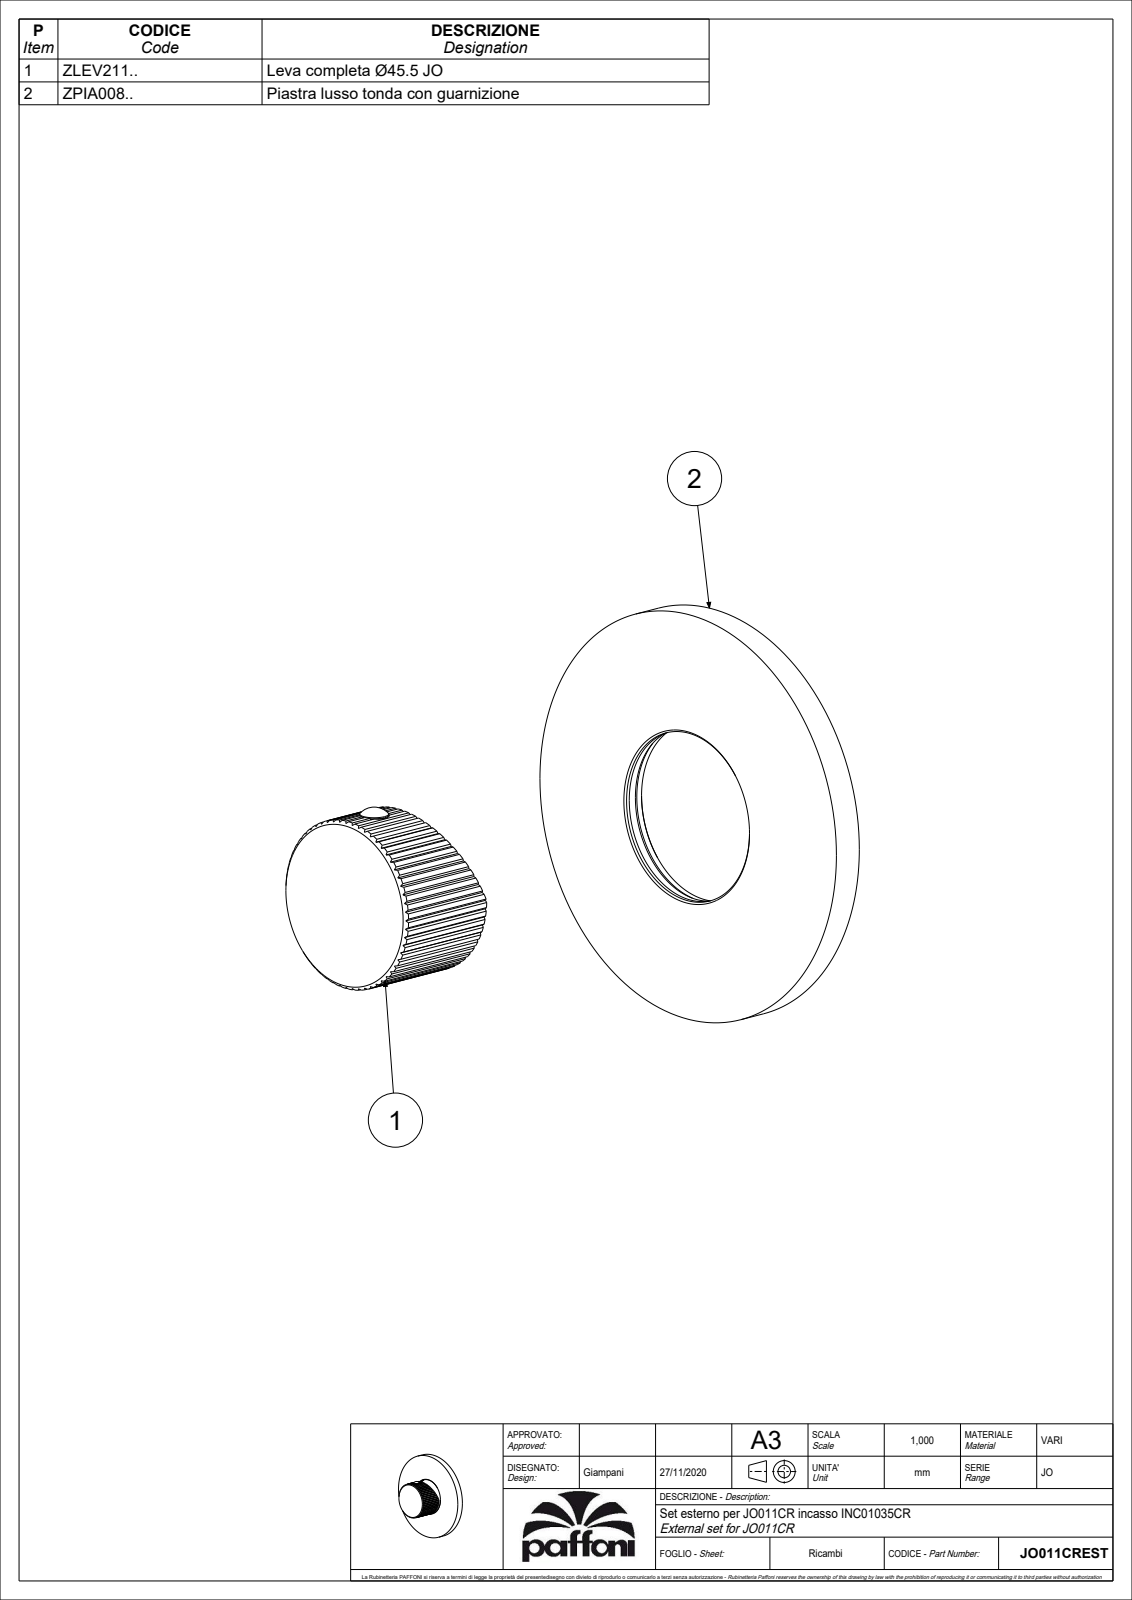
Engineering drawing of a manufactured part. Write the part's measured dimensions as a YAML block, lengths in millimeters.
part_name: "JO011CREST"
step_written_by: "CREO PARAMETRIC BY PTC INC, 2020044 (CONFIG_CONTROL_DESIGN)"
units: millimeters
bodies: {solids: 2, faces: 352, planar: 196, cylindrical: 121, other: 35}
overall_size: [110, 110, 41.4]
volume: 34849
surface_area: 36657
round_holes:
  - {diameter: 3, count: 1}
  - {diameter: 10.5, count: 1}
  - {diameter: 42, count: 1}
  - {diameter: 45.6, count: 1}
  - {diameter: 47.6, count: 1}
  - {diameter: 51.5, count: 1}
  - {diameter: 105, count: 1}
round_bosses_or_shafts:
  - {diameter: 110, count: 1}
  - {diameter: 54.6, count: 1}
  - {diameter: 16, count: 1}
  - {diameter: 7.6, count: 1}
  - {diameter: 5.5, count: 1}
  - {diameter: 5, count: 1}
partial_cylinders:
  - {radius: 4, count: 1}
  - {radius: 22.75, count: 1}
face_to_face_distances: [31, 7, 38, 1.5, 5.5, 36.5, 7.56, 6.06, 0.56, 30.44]
